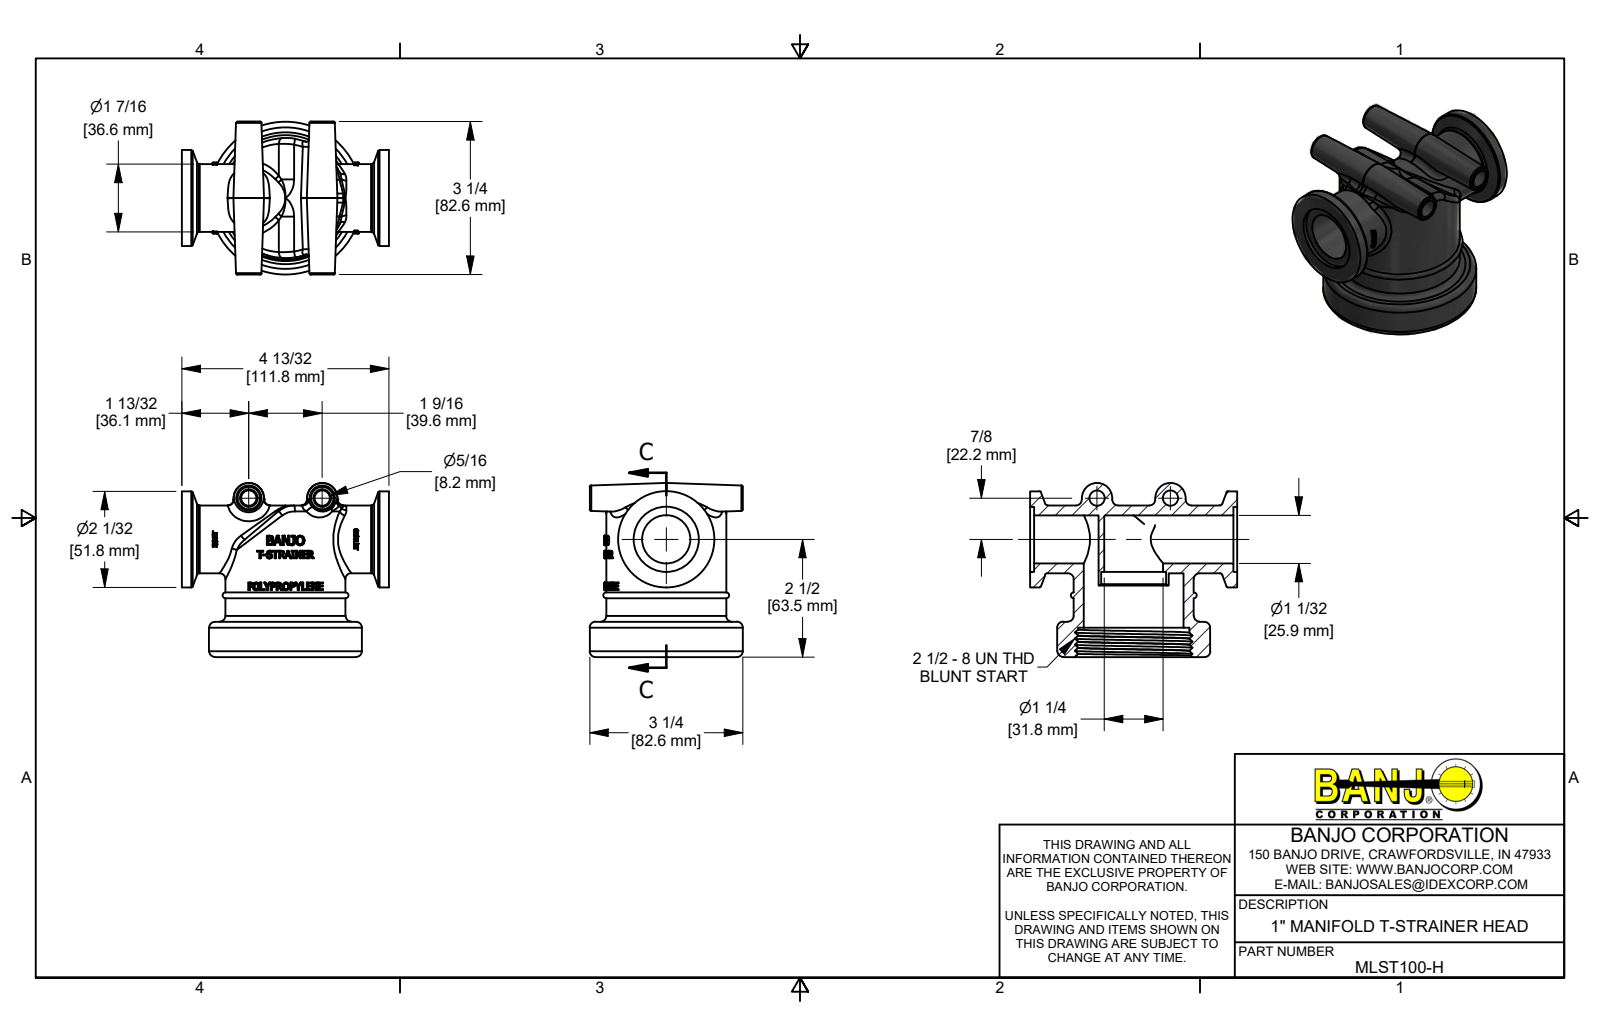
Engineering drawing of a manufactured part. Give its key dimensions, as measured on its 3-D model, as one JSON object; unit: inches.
{"part_name": "MLST100-H", "step_written_by": "Autodesk Inventor 2019 (AUTOMOTIVE_DESIGN)", "units": "inches", "bodies": {"solids": 1, "faces": 773, "planar": 391, "cylindrical": 89, "other": 293}, "overall_size": [4.4, 3.7, 3.25], "volume_in3": 11.18, "surface_area_in2": 111.6, "round_holes": [[1.38, 2], [1.02, 1], [1.25, 1], [2.12, 1], [2.365, 1]], "round_bosses_or_shafts": [[3.25, 1], [2.55, 1], [2.04, 1], [1.49, 1], [1.44, 1]], "partial_cylinders_radius": [[0.06, 1], [0.5, 1], [0.75, 1], [1.315, 1]], "face_to_face_distances": [4.4, 3.01, 0.084, 4.316, 0.75, 2.26, 0.625, 0.125, 2.385, 4.232]}
